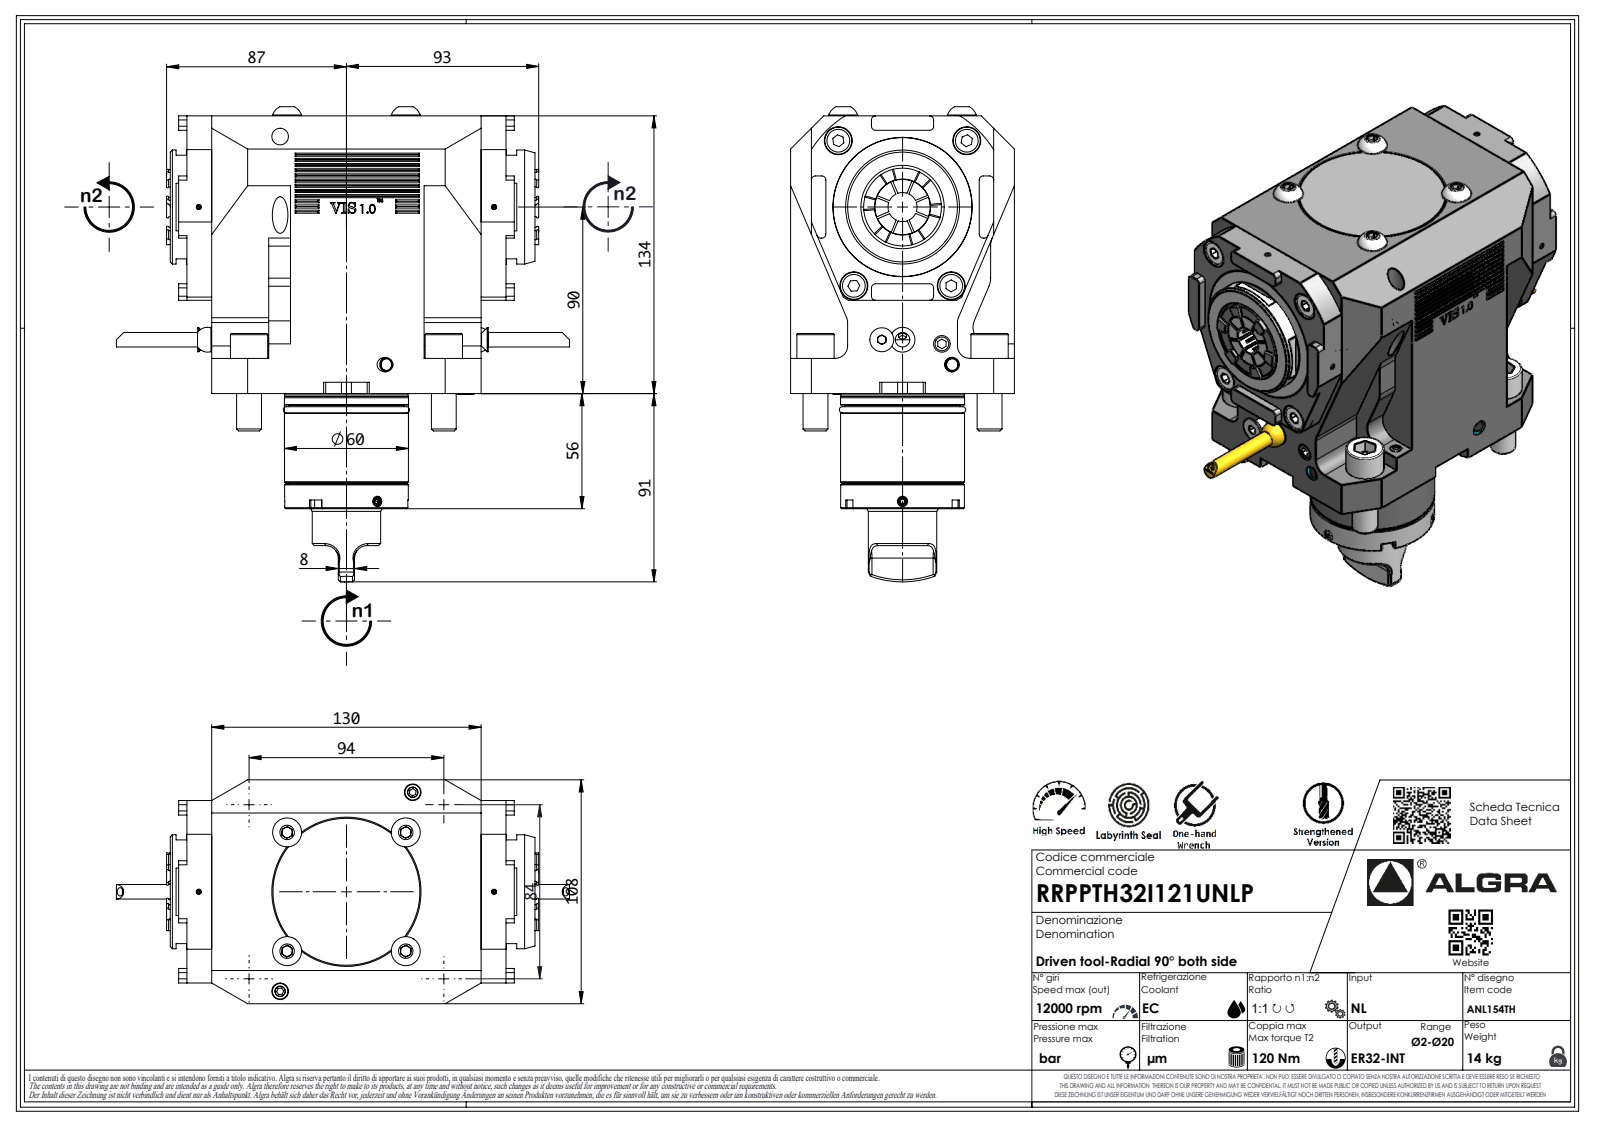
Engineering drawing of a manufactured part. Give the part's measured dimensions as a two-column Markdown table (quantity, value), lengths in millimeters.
| quantity | value |
| --- | --- |
| part name | RRPPTH32I121UNLP |
| STEP written by | SolidWorks 2023 (AUTOMOTIVE_DESIGN) |
| units | millimeters |
| bodies | 1 solid, 1109 faces (703 planar, 174 cylindrical, 232 other) |
| overall size | 224.8 × 218.64 × 108 |
| volume | 2 069 000 mm³ |
| surface area | 131 174 mm² |
| round holes (diameter × count) | 4 × 2, 2.1 × 1 |
| round bosses / shafts (diameter × count) | 18 × 4, 12 × 4, 59.9 × 1, 59.8 × 1, 59.7 × 1, 59.5 × 1, 55.2 × 1, 55 × 1 |
| partial cylindrical surfaces (radius × count) | 0.2 × 21, 8 × 18, 2 × 16, 6 × 10, 0.33 × 7, 0.52 × 7, 3.7 × 7, 10 × 4 |
| main face-to-face distances | 108, 12, 134, 142, 39.5, 27.5, 128.5, 114.5, 102.5, 154 |
